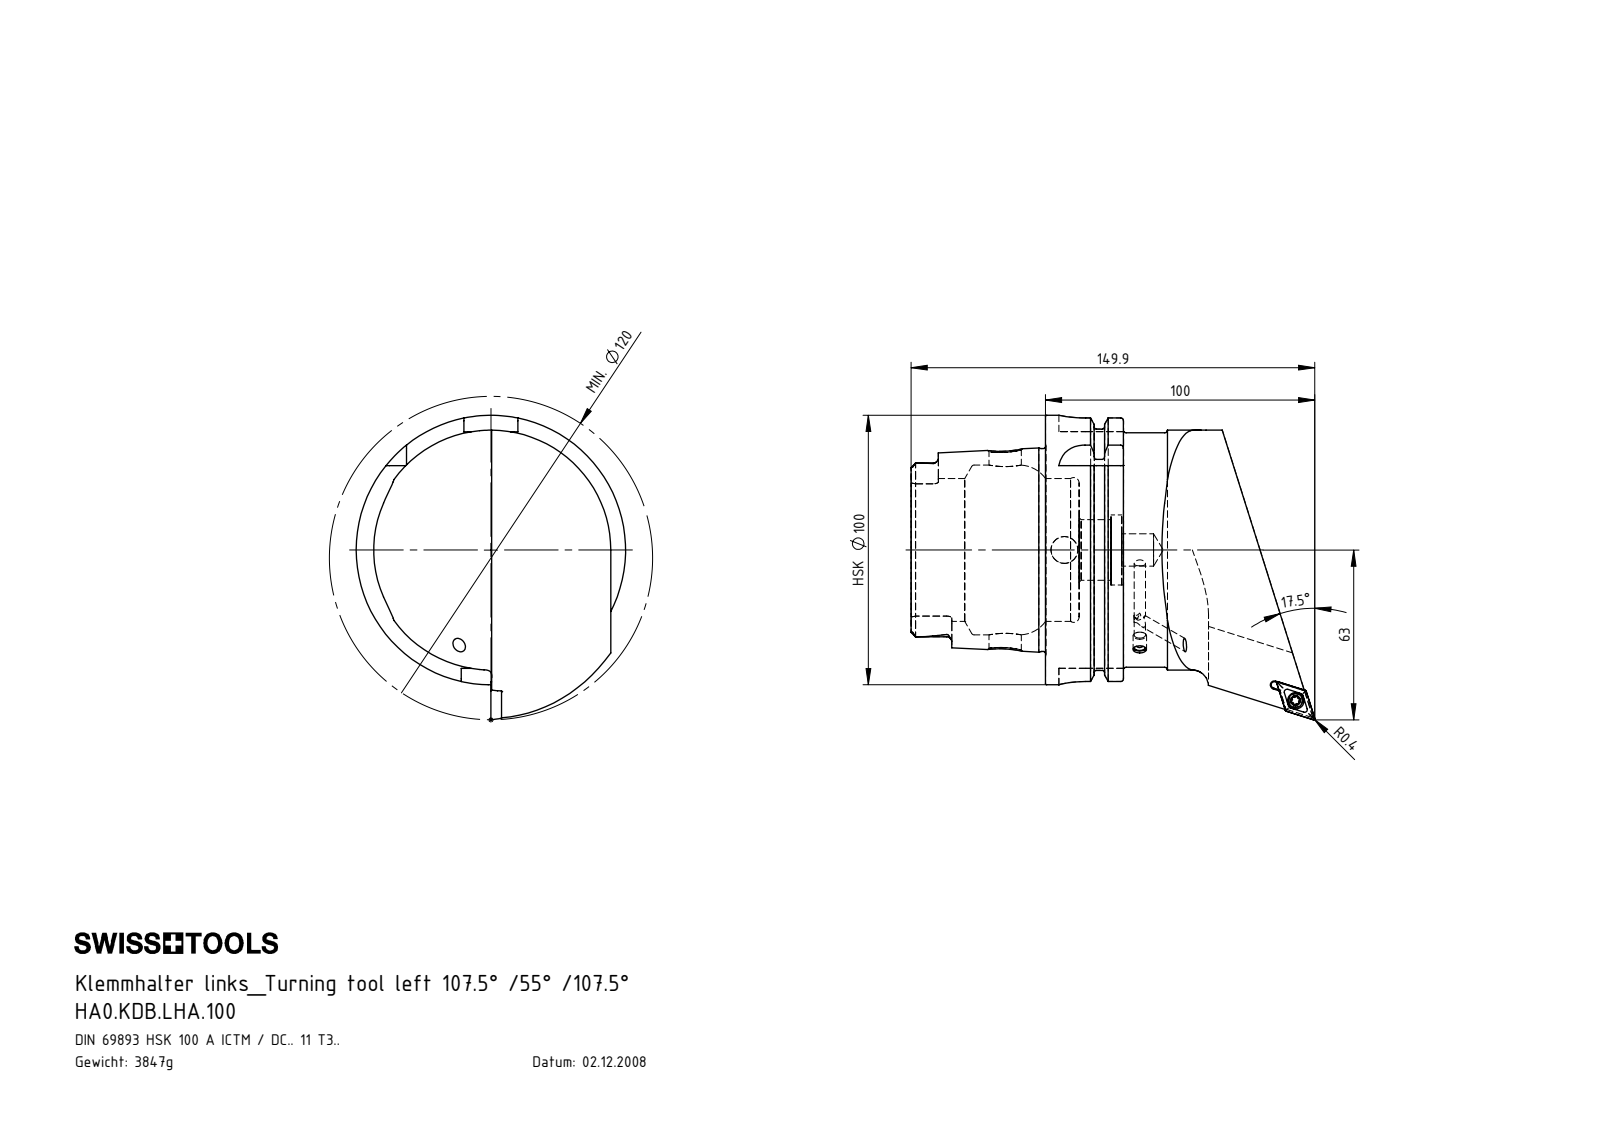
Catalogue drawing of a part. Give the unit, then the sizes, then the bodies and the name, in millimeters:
Units: millimetres
Overall size (bounding box): 149.91 × 113 × 100
Round holes (diameter × count): ⌀4.2 ×2, ⌀12 ×2, ⌀3.3 ×1, ⌀4 ×1, ⌀4.4 ×1, ⌀6.1 ×1, ⌀10 ×1, ⌀22.5 ×1, ⌀26 ×1, ⌀53 ×1, ⌀63 ×1
Round bosses / shafts (diameter × count): ⌀100 ×1, ⌀91.95 ×1, ⌀89 ×1, ⌀87 ×1, ⌀75.26 ×1, ⌀5.25 ×1, ⌀5 ×1, ⌀4 ×1
Partial cylindrical surfaces — rounded edges, fillets, slot ends (radius × count): R0.34 ×6, R0.59 ×6, R1.9 ×6, R10 ×4, R4.83 ×2, R4.88 ×2, R1.25 ×1, R6 ×1
Main face-to-face distances: 12.45, 28.95, 16.5, 49.9, 62.35, 78.85, 44.2, 87.8, 78.2, 28.3
Hole centre spacings: 102.39, 102.51
Volume: 489 781 mm³ · Surface area: 66 168 mm²
Bodies: 5 solids, 309 faces (73 planar, 93 cylindrical, 143 other)
Part name (STEP PRODUCT): DCMT11T304; WCB-ER2.001.009_A; KVT_MB_600_050; HA0-KDB.LHA.100_A_Fertigbearbeitung (+1 more)
STEP written by: SolidWorks 2012 (AUTOMOTIVE_DESIGN)
